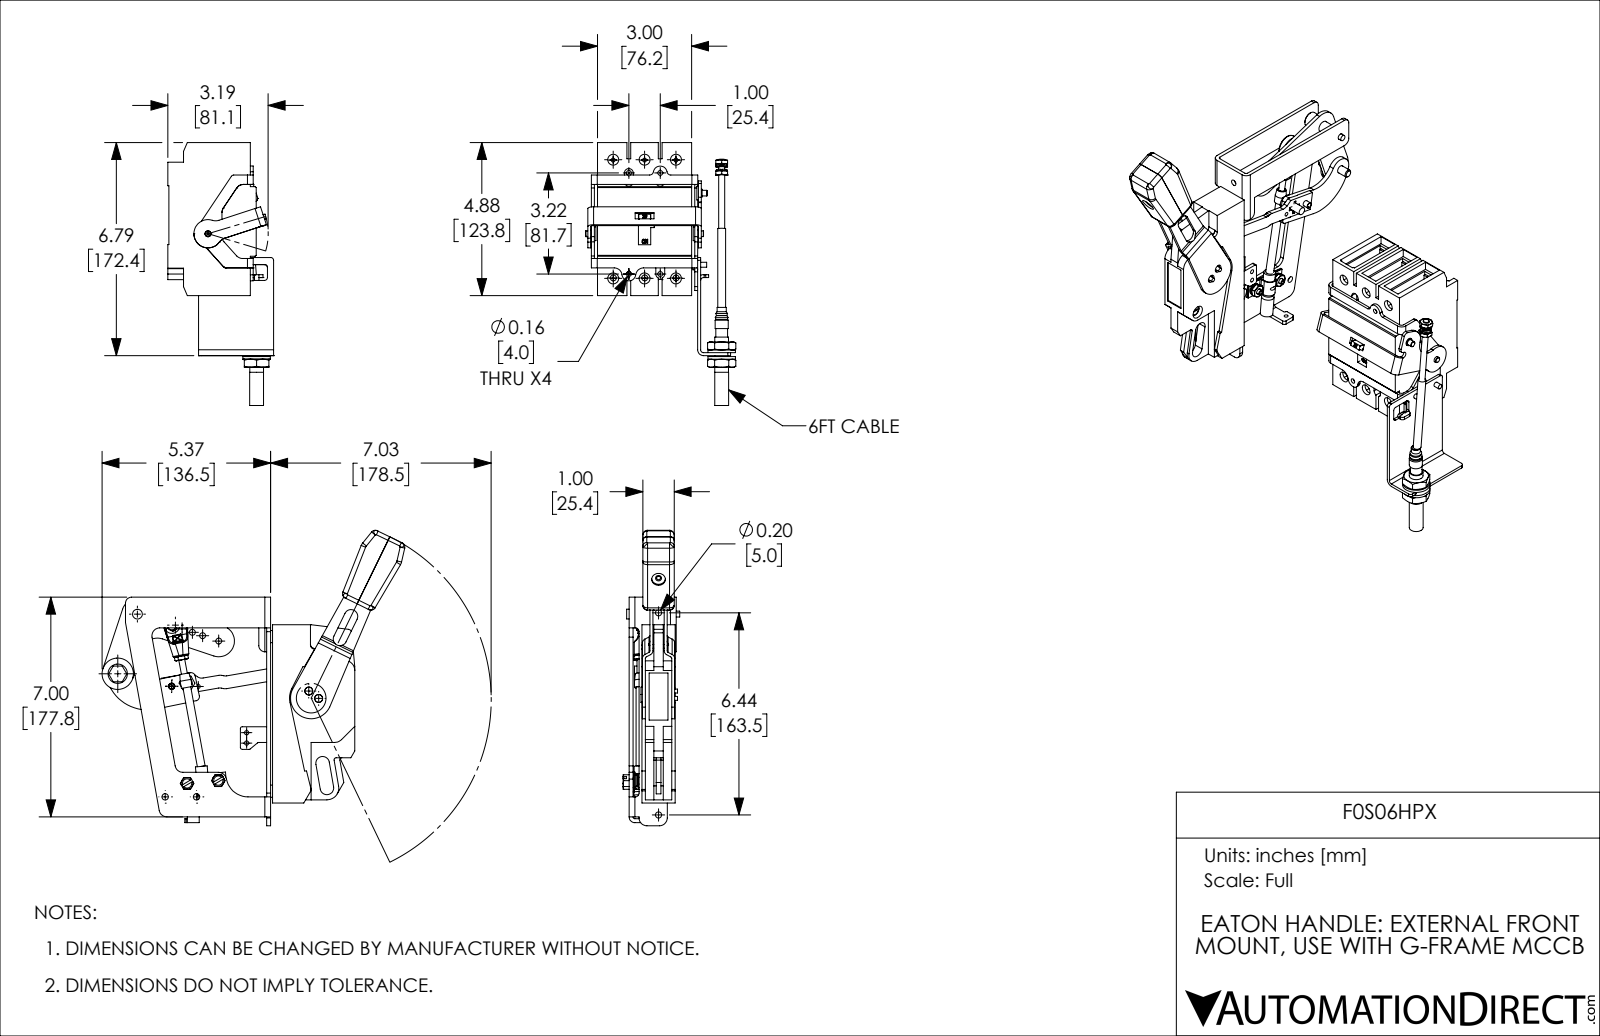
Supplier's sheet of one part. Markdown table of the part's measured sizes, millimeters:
| quantity | value |
| --- | --- |
| part name | F0S06HPX_BREAKER; F0S06HPX; F0S06HPX_HANDLE |
| STEP written by | SolidWorks 2019 (CONFIG_CONTROL_DESIGN) |
| units | millimeters |
| bodies | 77 solids, 2152 faces (1122 planar, 779 cylindrical, 251 other) |
| overall size | 297.4 × 255.7 × 245.1 |
| volume | 838 000 mm³ |
| surface area | 282 300 mm² |
| round holes (diameter × count) | 4 × 8, 4.8 × 8, 5.2 × 6, 8.8 × 6, 4.8 × 5, 3.2 × 3, 3.2 × 3, 4.9 × 3, 5 × 3, 6.4 × 3, 6.4 × 3, 3.5 × 2 |
| round bosses / shafts (diameter × count) | 6.4 × 9, 9.5 × 5, 11.2 × 4, 9.5 × 3, 8.7 × 3, 7.9 × 3, 6.2 × 3, 4.6 × 3 |
| partial cylindrical surfaces (radius × count) | 6.4 × 31, 2.3 × 23, 1.6 × 17, 3.2 × 17, 0.5 × 12, 3.8 × 12, 0.8 × 11, 0.8 × 10 |
| main face-to-face distances | 2.4, 3.2, 15.1, 135.7, 211.9, 76.2, 138.9, 215.1, 4.7, 2.8 |
| hole center spacings | 25.4, 50.8, 0.4, 16.4, 86.3, 93, 99.1, 141.5 |
